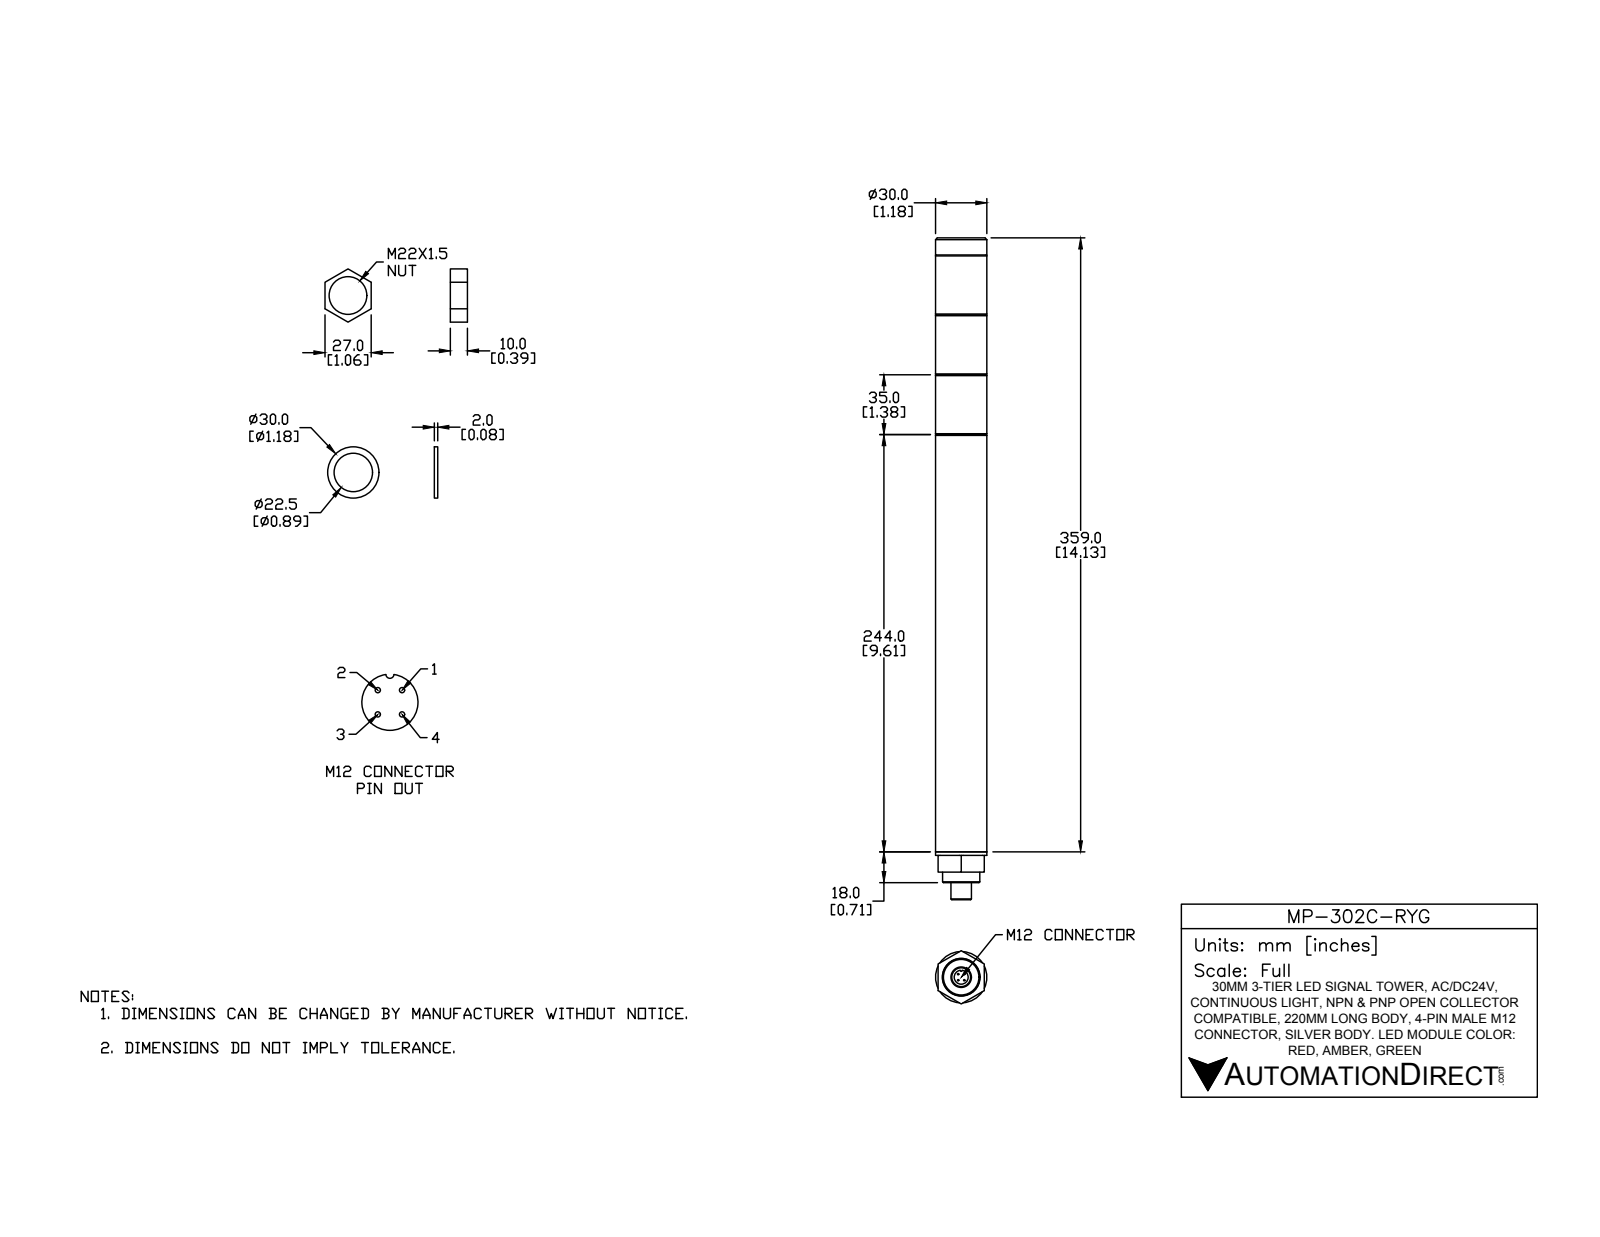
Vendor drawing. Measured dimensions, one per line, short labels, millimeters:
name: MP-302C-RYG
written by: SolidWorks 2016 (AUTOMOTIVE_DESIGN)
unit: mm
bodies: 12 solids, 114 faces (45 planar, 39 cylindrical, 30 other)
size: 387 × 31.18 × 30
volume: 252 898 mm³; area: 48 666 mm²
holes: 1× ⌀3.2, 1× ⌀7.7, 1× ⌀8.2, 1× ⌀20.7, 1× ⌀22
bosses: 4× ⌀0.75, 1× ⌀30, 1× ⌀21.8, 1× ⌀12, 1× ⌀5
rounds: 1× R0.6
face distances: 35, 70, 105, 244, 279, 314, 349, 246, 281, 316
